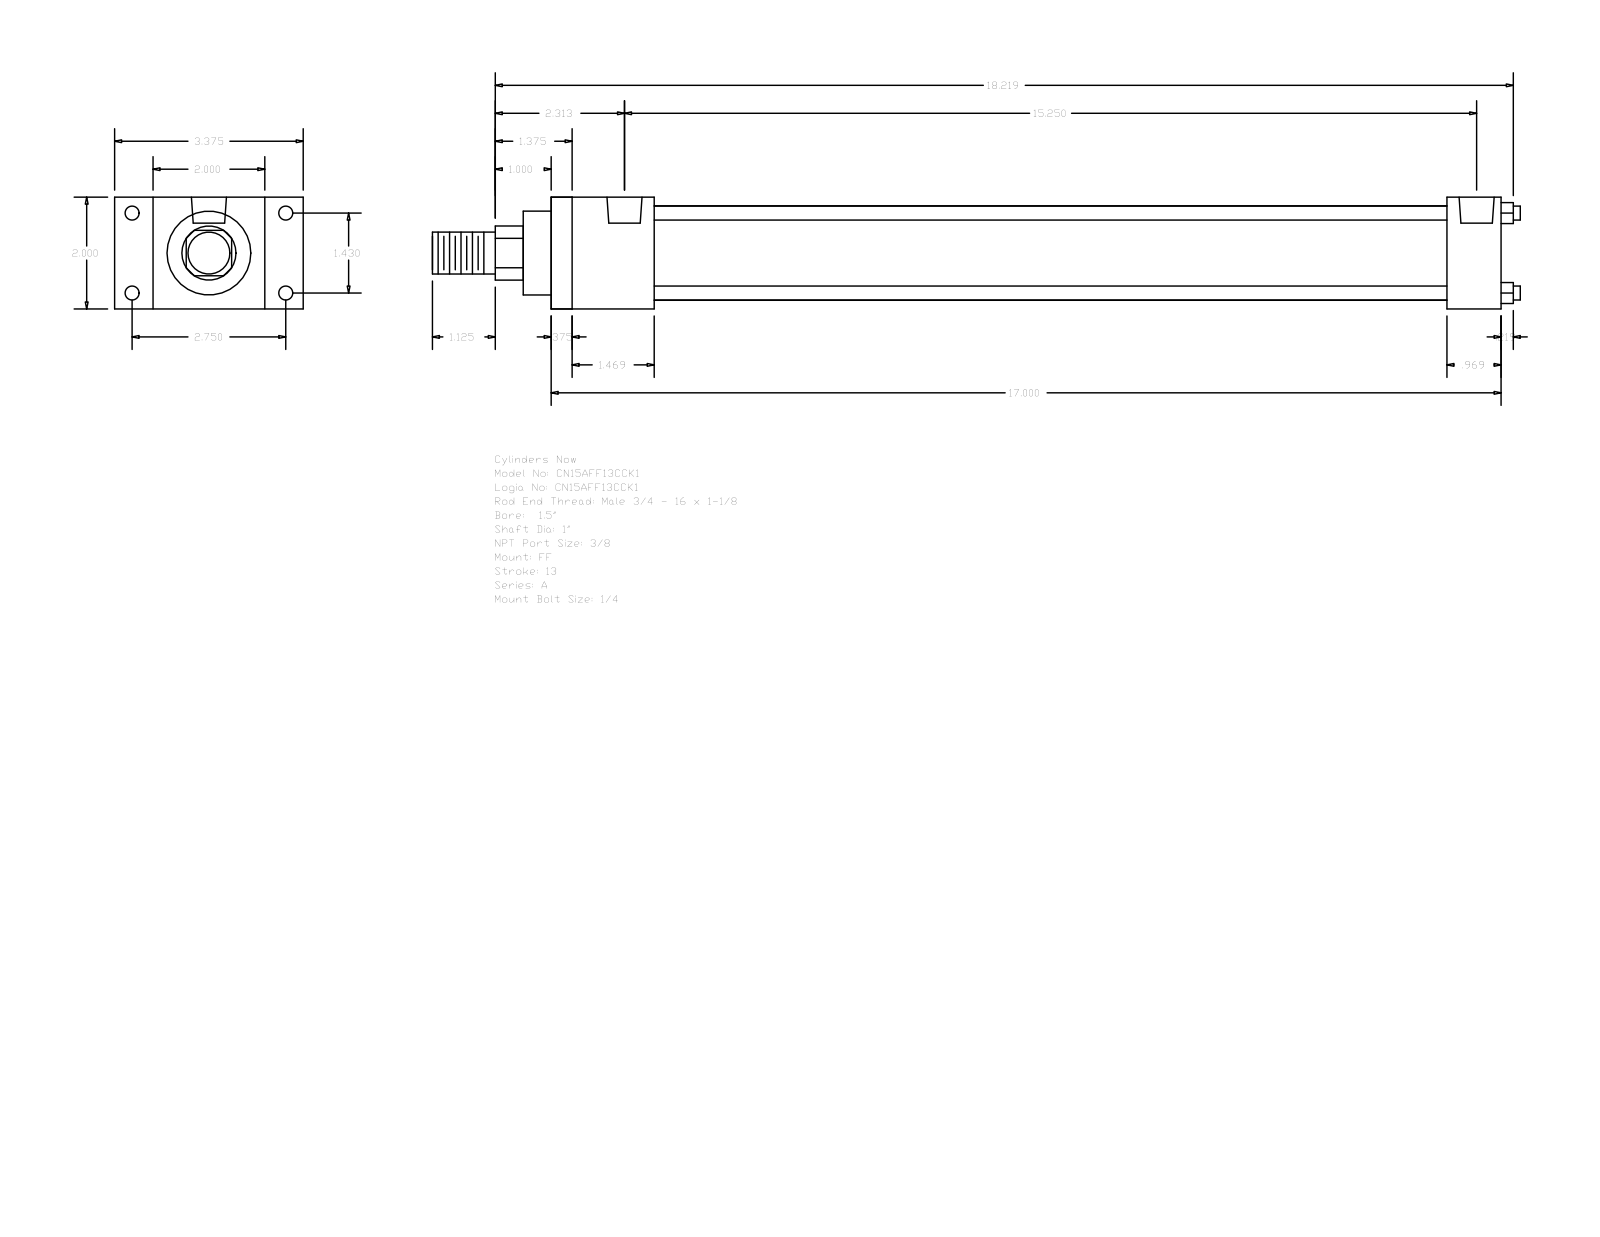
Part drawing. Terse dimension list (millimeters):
name: A_FF__0150_1
written by: GSSL Pune (CONFIG_CONTROL_DESIGN)
unit: mm
bodies: 0 solids, 92 faces (64 planar, 28 cylindrical, 0 other)
size: 494.51 × 85.72 × 50.8
holes: 4× ⌀5.56, 4× ⌀6.35, 2× ⌀15.93
bosses: 4× ⌀6.35, 1× ⌀42.93, 1× ⌀38.1, 1× ⌀25.4, 1× ⌀19.05
rounds: 1× R12.29
face distances: 50.8, 431.8, 9.52, 422.28, 46.83, 407.19, 37.31, 397.67, 360.36, 384.97
hole spacings: 3.97, 36.32, 69.84, 78.72, 379.41, 383.38, 387.35
